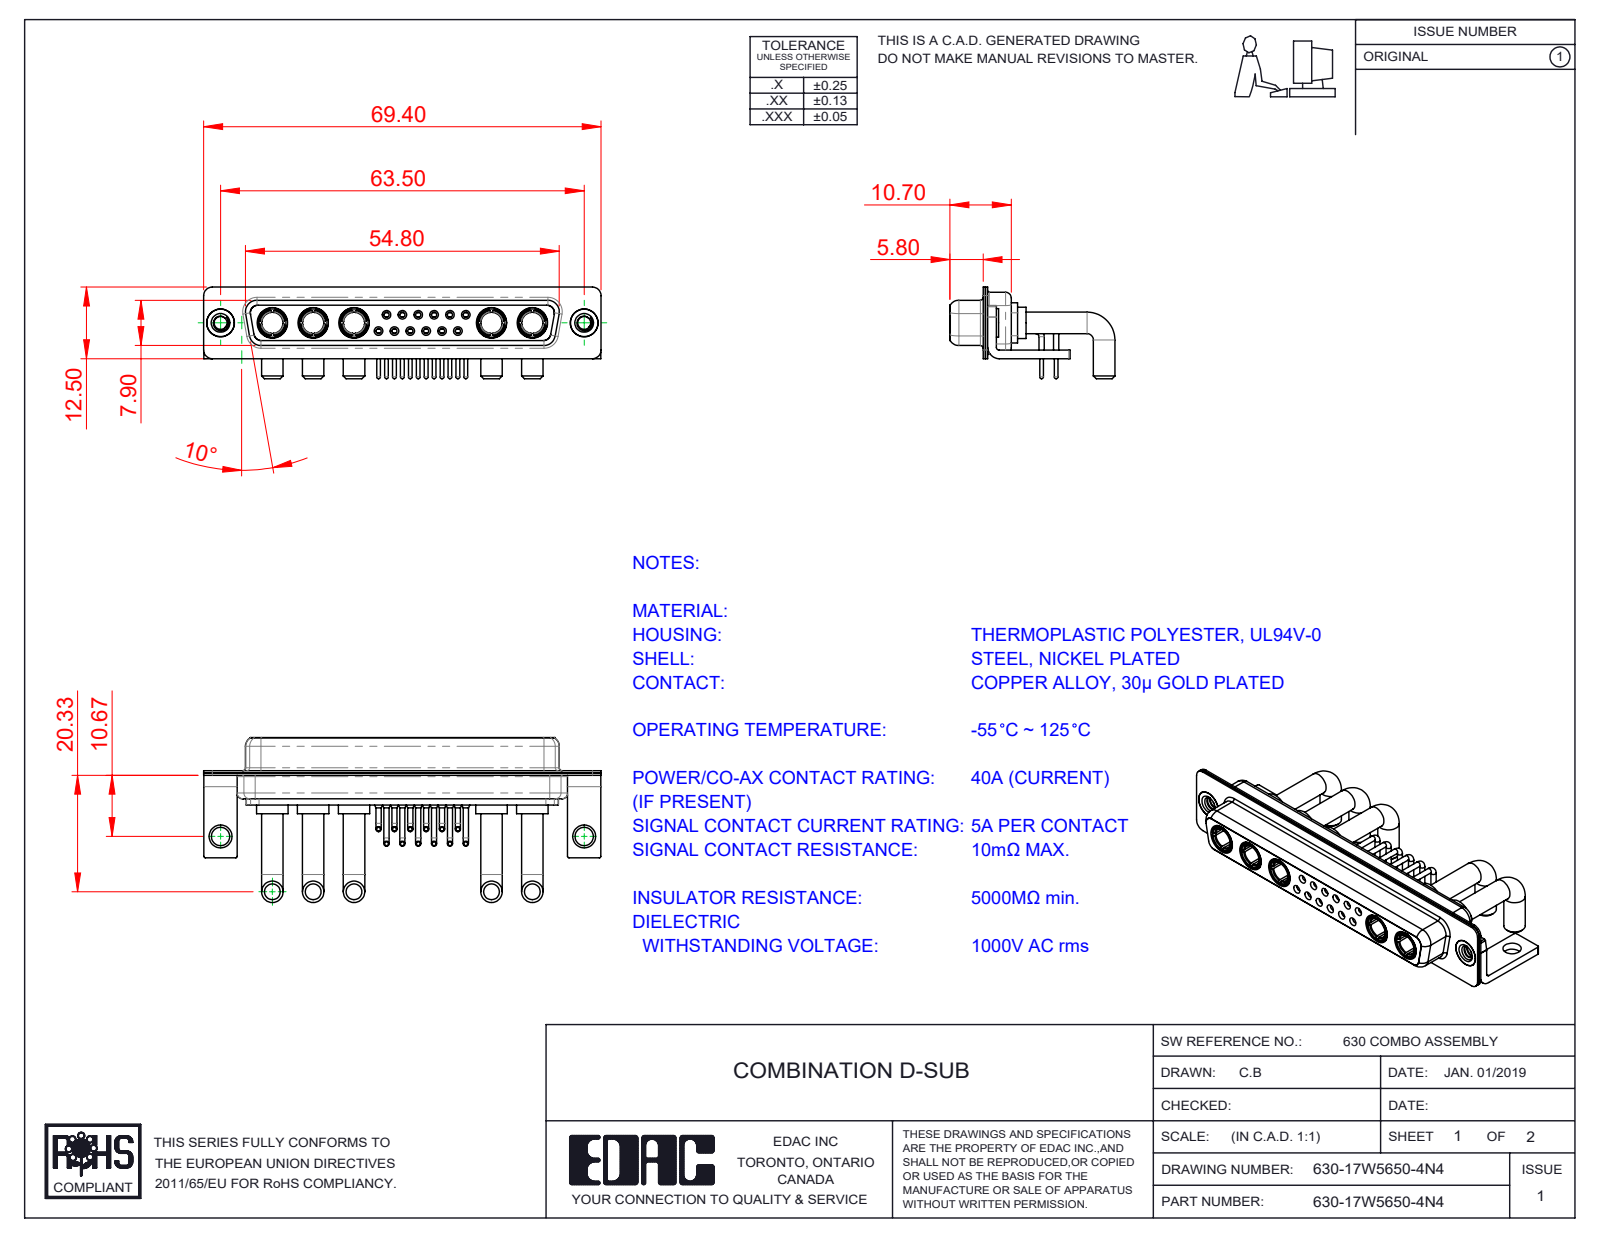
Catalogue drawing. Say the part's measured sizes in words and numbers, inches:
The part is named "Power Socket_Ext 40A RA; 630Combo Shell Rear_37 Contacts; 630-17W5650-4N4; 630Combo Housing_17W5 (+5 more)". Its 3-D file was written by "SolidWorks 2020 (CONFIG_CONTROL_DESIGN)". It is 29 solids with 1345 faces: 412 planar, 556 cylindrical and 377 other. Overall it measures 2.732 by 1.134 by 0.63 inches. Its volume is 0.409 cubic inches and its surface area 21.09 square inches. Round holes: 12 of diameter 0.035, 12 of diameter 0.043, 12 of diameter 0.059, 12 of diameter 0.079, 7 of diameter 0.191, 6 of diameter 0.063, 6 of diameter 0.067, 5 of diameter 0.146, 5 of diameter 0.209, 2 of diameter 0.089, 2 of diameter 0.126, 2 of diameter 0.157. Round bosses or shafts: 13 of diameter 0.035, 12 of diameter 0.026, 10 of diameter 0.148, 7 of diameter 0.063, 5 of diameter 0.217, 5 of diameter 0.205, 5 of diameter 0.195, 5 of diameter 0.187. Partial cylindrical surfaces (rounded edges, fillets, slot ends): 16 of radius 0.01, 16 of radius 0.059, 13 of radius 0.079, 8 of radius 0.053, 8 of radius 0.063, 5 of radius 0.02, 5 of radius 0.083, 4 of radius 0.024. The main face-to-face distances are 0.016, 0.018, 0.055, 0.333, 0.071, 0.35, 0.244, 0.278, 0.031, 0.053. The hole center spacings are 0.124, 0.109, 0.198, 0.218, 0.198, 0.295, 0.327, 0.398.
